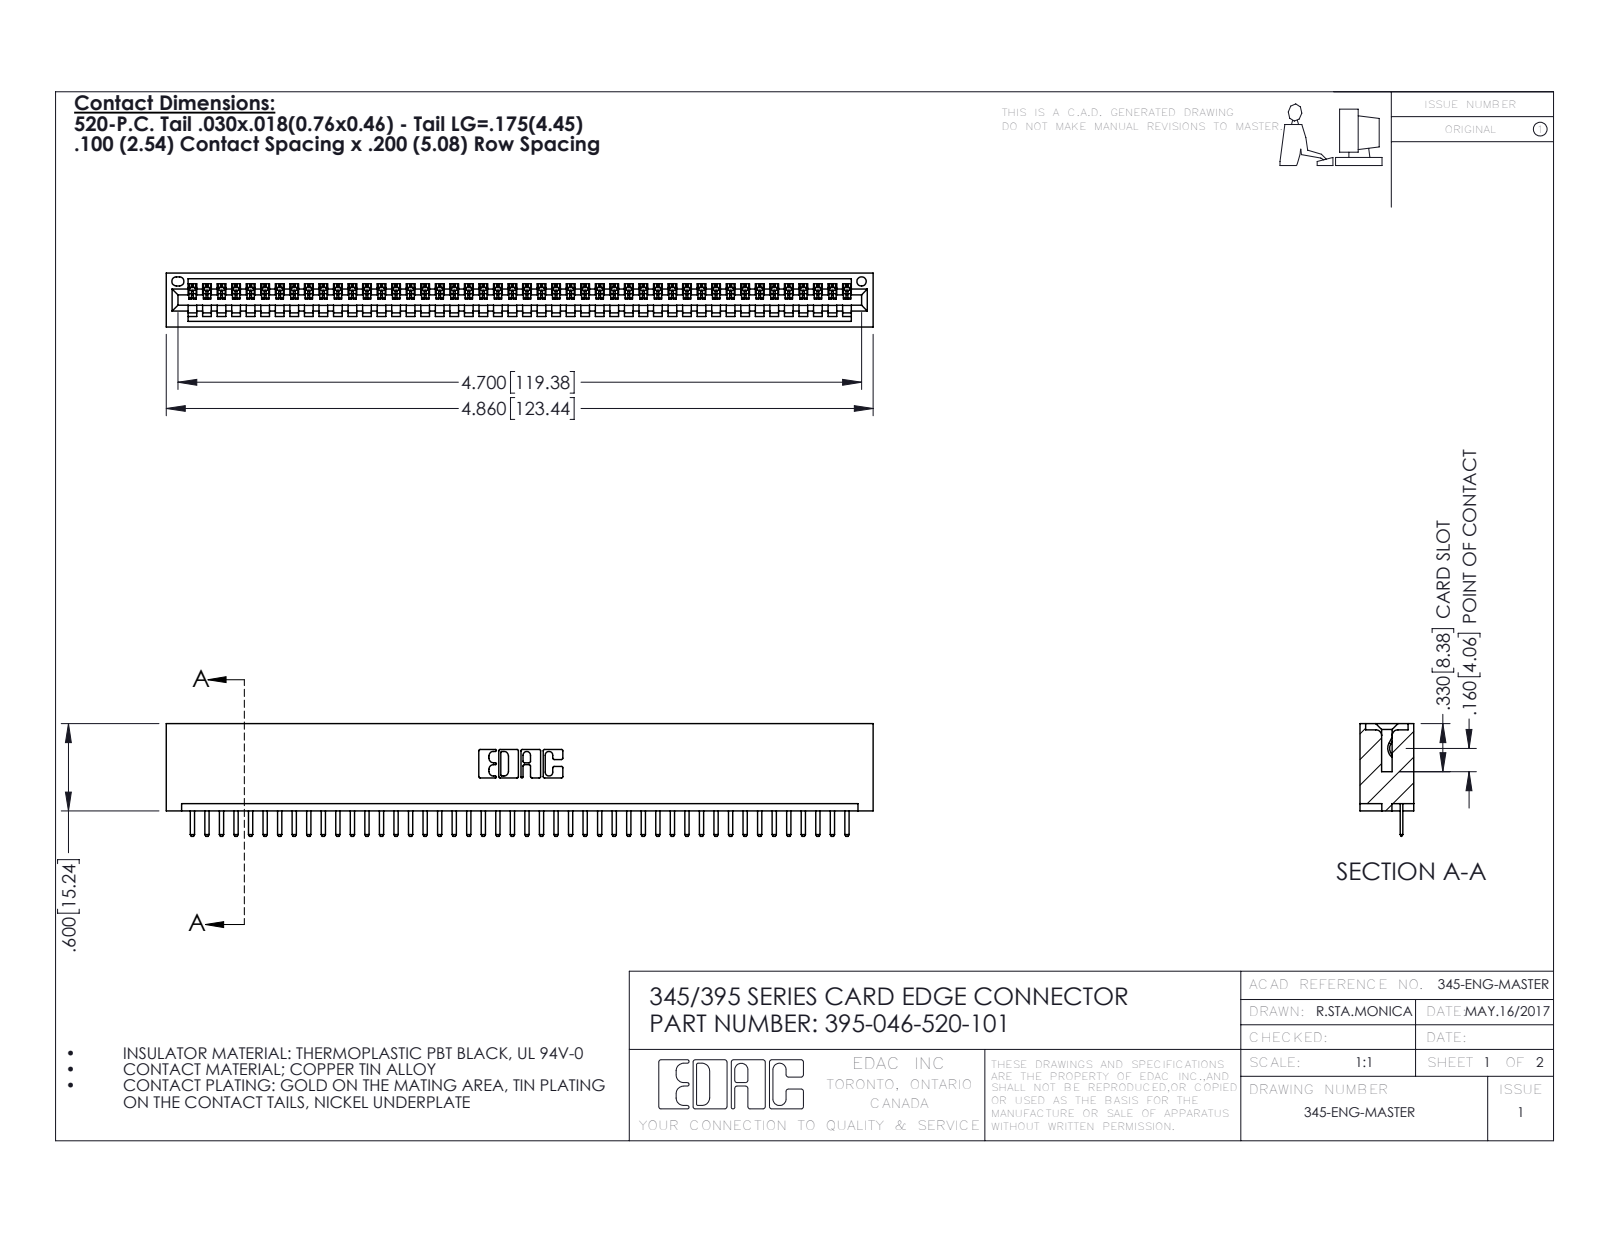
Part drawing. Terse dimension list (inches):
name: 345-292-001_345-293-120; 345 Part_No Mounting Lugs; 395-046-520-101
written by: SolidWorks 2016 (CONFIG_CONTROL_DESIGN)
unit: in
bodies: 47 solids, 2970 faces (2008 planar, 962 cylindrical, 0 other)
size: 4.86 × 0.775 × 0.37
volume: 0.745 in³; area: 24.86 in²
holes: 1× ⌀0.064
rounds: 94× R0.01, 92× R0.006, 22× R0.01, 6× R0.007, 6× R0.031, 3× R0.026, 2× R0.031, 2× R0.04
face distances: 0.298, 0.072, 0.37, 0.2, 0.098, 0.272, 0.025, 0.225, 0.072, 0.149
